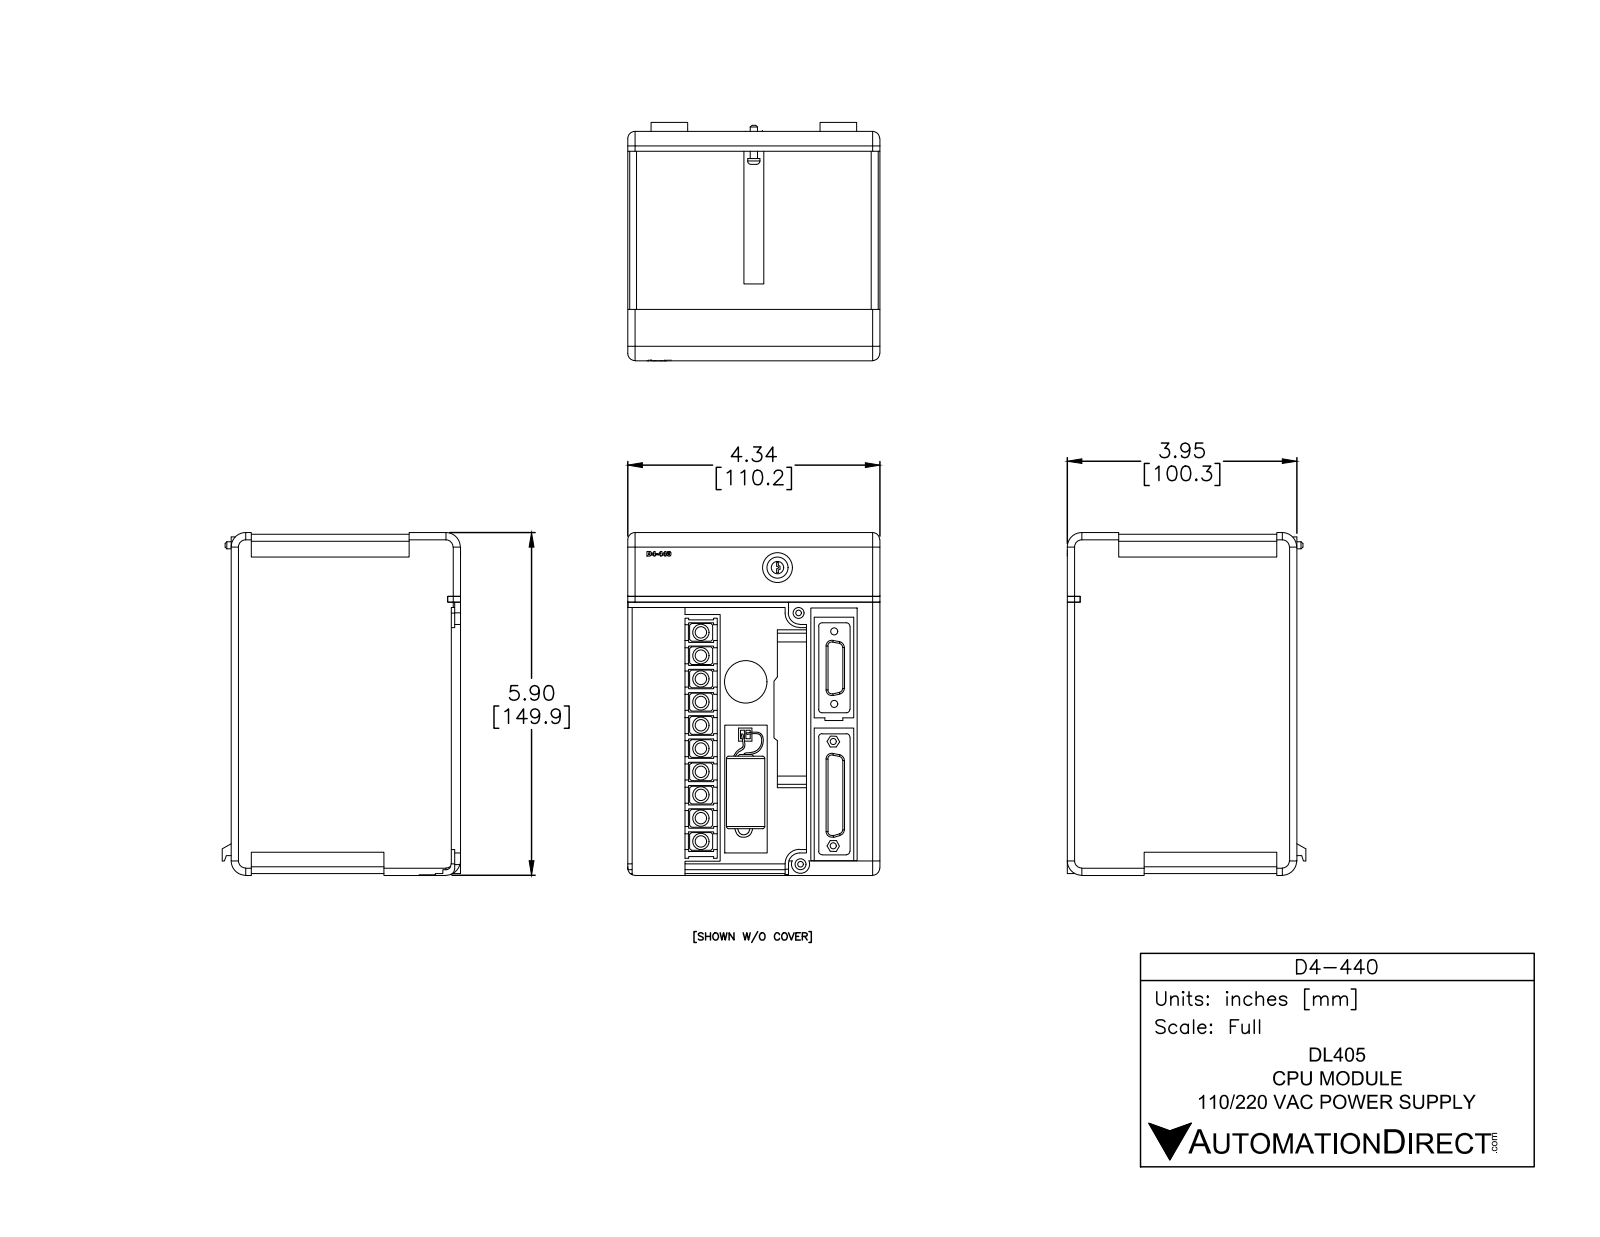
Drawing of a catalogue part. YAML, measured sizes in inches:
part_name: "D4-440"
step_written_by: "SolidWorks 2014 (AUTOMOTIVE_DESIGN)"
units: inches
bodies: {solids: 3, faces: 734, planar: 564, cylindrical: 111, other: 59}
overall_size: [5.905, 4.34, 4.106]
volume: 90.72
surface_area: 177.8
round_holes:
  - {diameter: 0.1, count: 2}
  - {diameter: 0.12, count: 2}
  - {diameter: 0.104, count: 1}
  - {diameter: 0.105, count: 1}
  - {diameter: 0.188, count: 1}
  - {diameter: 0.188, count: 1}
  - {diameter: 0.216, count: 1}
  - {diameter: 0.51, count: 1}
  - {diameter: 0.73, count: 1}
round_bosses_or_shafts:
  - {diameter: 0.279, count: 10}
  - {diameter: 0.66, count: 1}
  - {diameter: 0.365, count: 1}
  - {diameter: 0.212, count: 1}
  - {diameter: 0.123, count: 1}
partial_cylinders:
  - {radius: 0.1, count: 9}
  - {radius: 0.06, count: 8}
  - {radius: 0.125, count: 8}
  - {radius: 0.03, count: 6}
  - {radius: 0.25, count: 6}
  - {radius: 0.12, count: 4}
  - {radius: 0.2, count: 2}
  - {radius: 0.145, count: 1}
face_to_face_distances: [4.34, 0.03, 5.845, 5.875, 3.95, 0.715, 3.235, 0.45, 3.79, 0.555]
hole_center_spacings: [0.644, 0.649, 0.69, 0.861, 1.248, 1.47, 1.497, 1.569]
